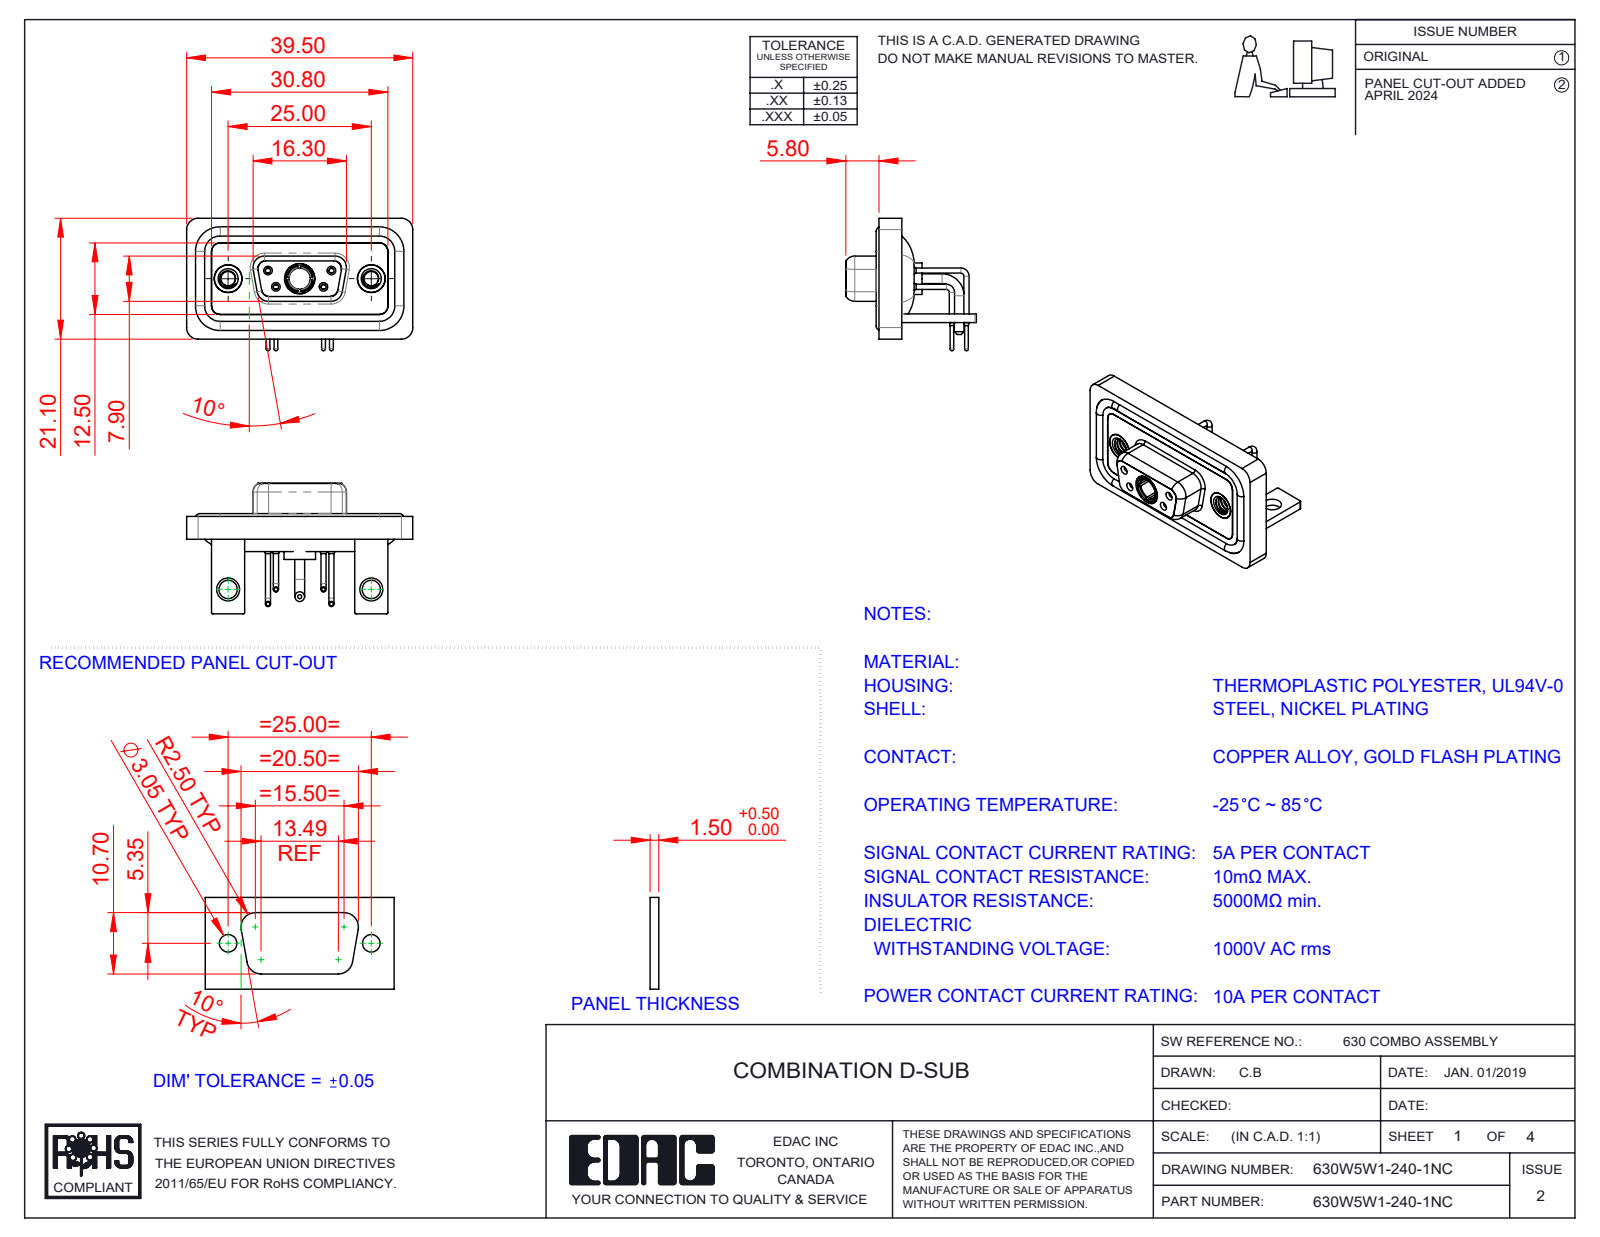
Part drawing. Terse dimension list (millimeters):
name: 630Combo Threaded Rivet_A; 630Combo Housing_5W1; 630Combo Stabilizer Bracket_50 Contacts; 630Combo Contact Row 2_50 Contacts (+6 more)
written by: SolidWorks 2023 (CONFIG_CONTROL_DESIGN)
unit: mm
bodies: 15 solids, 718 faces (214 planar, 327 cylindrical, 177 other)
size: 39.5 × 23.12 × 22.8
volume: 5 130 mm³; area: 8 531 mm²
holes: 4× ⌀0.9, 4× ⌀1.1, 4× ⌀1.5, 4× ⌀2, 3× ⌀4.85, 2× ⌀1.6, 2× ⌀1.7, 2× ⌀2.5, 2× ⌀3.2, 2× ⌀4, 2× ⌀4.05, 2× ⌀5
bosses: 6× ⌀1.6, 4× ⌀0.9, 4× ⌀0.65, 2× ⌀4.95, 2× ⌀4.8, 2× ⌀1.7, 1× ⌀5.5, 1× ⌀5.2
rounds: 19× R2, 18× R1.5, 16× R0.25, 8× R1.35, 8× R1.6, 5× R0.5, 4× R0.6, 4× R0.65
face distances: 0.4, 2.9, 1.5, 1.8, 1.1, 3.7, 1.6, 0.8, 2.5, 3.1
hole spacings: 3.16, 5.72, 7.1, 12.5, 18.1, 25, 4.39, 4.4
